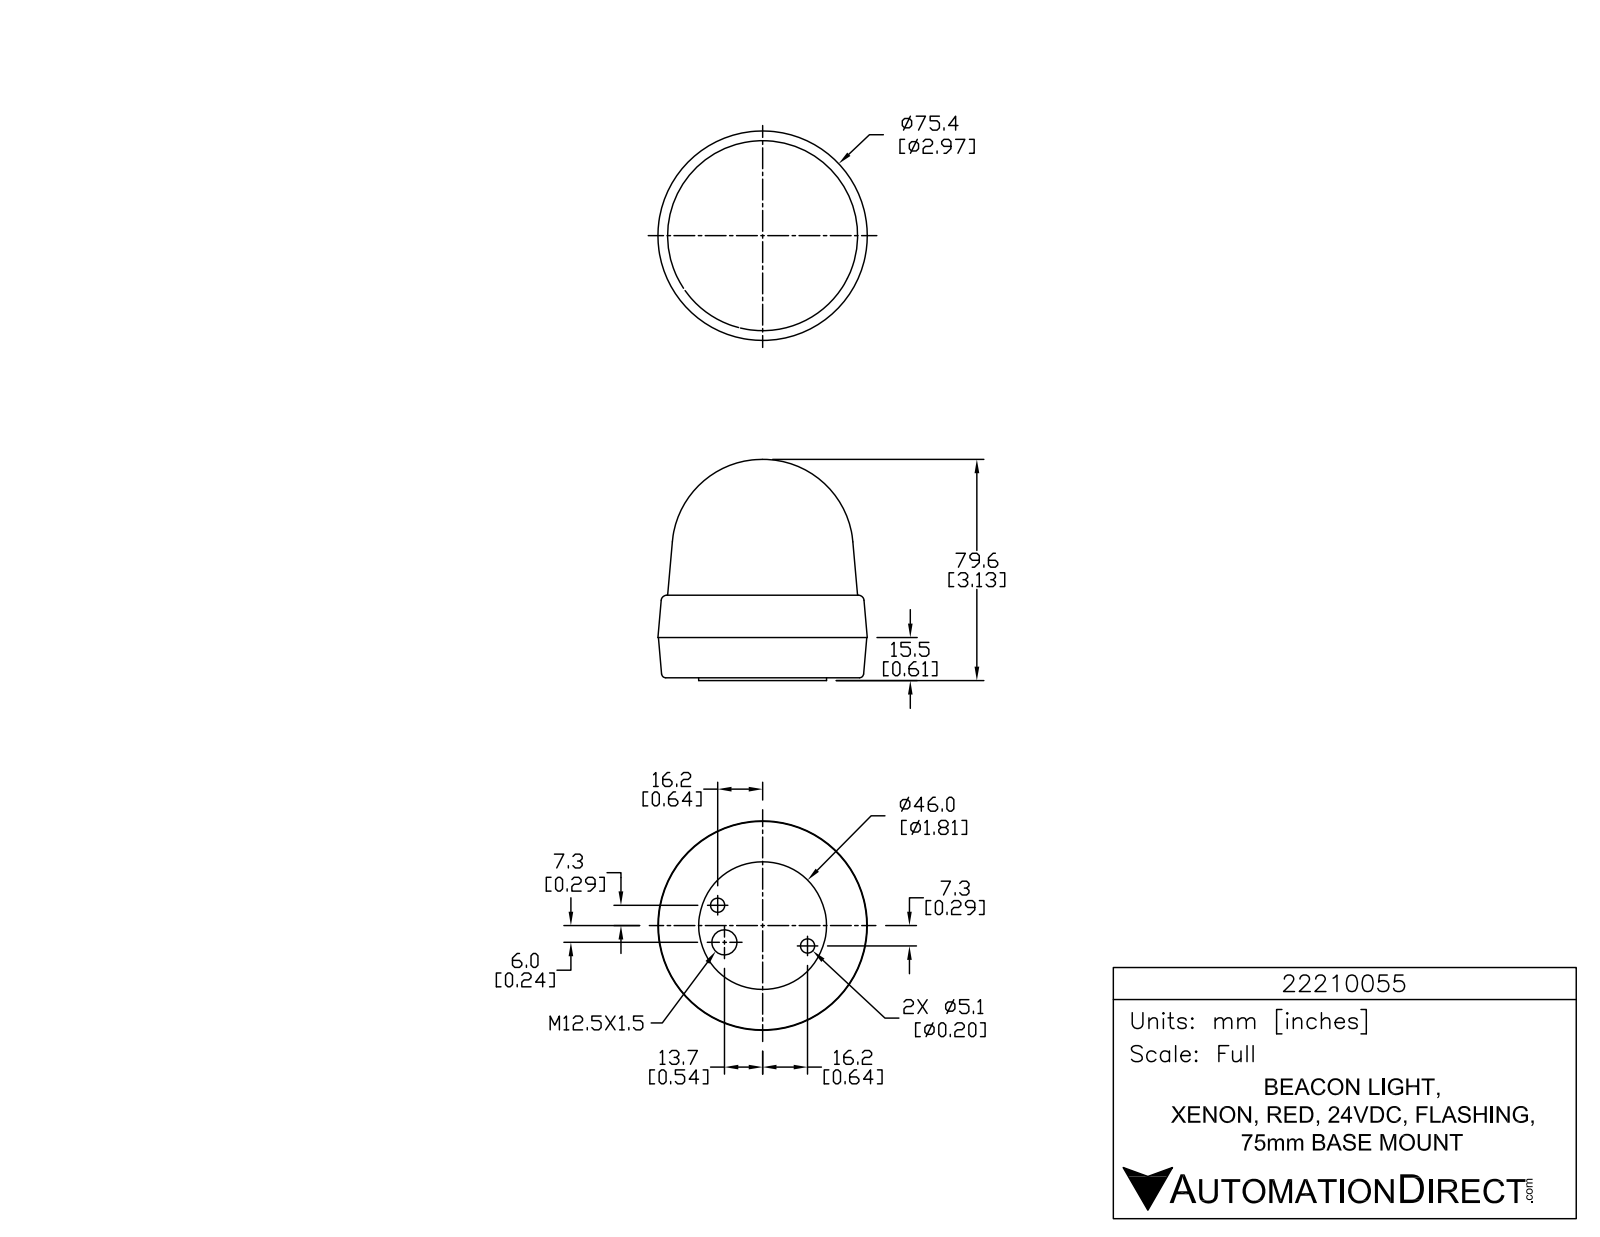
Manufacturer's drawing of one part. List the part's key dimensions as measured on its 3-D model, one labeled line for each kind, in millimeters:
Part name (STEP PRODUCT): 22210055
STEP written by: SolidWorks 2015 (AUTOMOTIVE_DESIGN)
Units: millimetres
Bodies: 1 solid, 773 faces (526 planar, 163 cylindrical, 84 other)
Overall size (bounding box): 79.6 × 75.4 × 75.4
Volume: 258 800 mm³ · Surface area: 21 740 mm²
Round holes (diameter × count): ⌀1.5 ×3, ⌀5.1 ×2, ⌀9 ×1
Round bosses / shafts (diameter × count): ⌀8.6 ×3, ⌀2.1 ×3, ⌀46 ×1
Partial cylindrical surfaces — rounded edges, fillets, slot ends (radius × count): R0.1 ×9, R0.1 ×6, R0.3 ×6, R0.3 ×6, R0.3 ×6, R5 ×6, R0.1 ×3, R0.1 ×3
Main face-to-face distances: 1, 30.7, 29.7, 15.5, 14.5, 15.2, 39.8, 38.8, 24.3, 9.1
Hole centre spacings: 13.6, 29.9, 35.5
